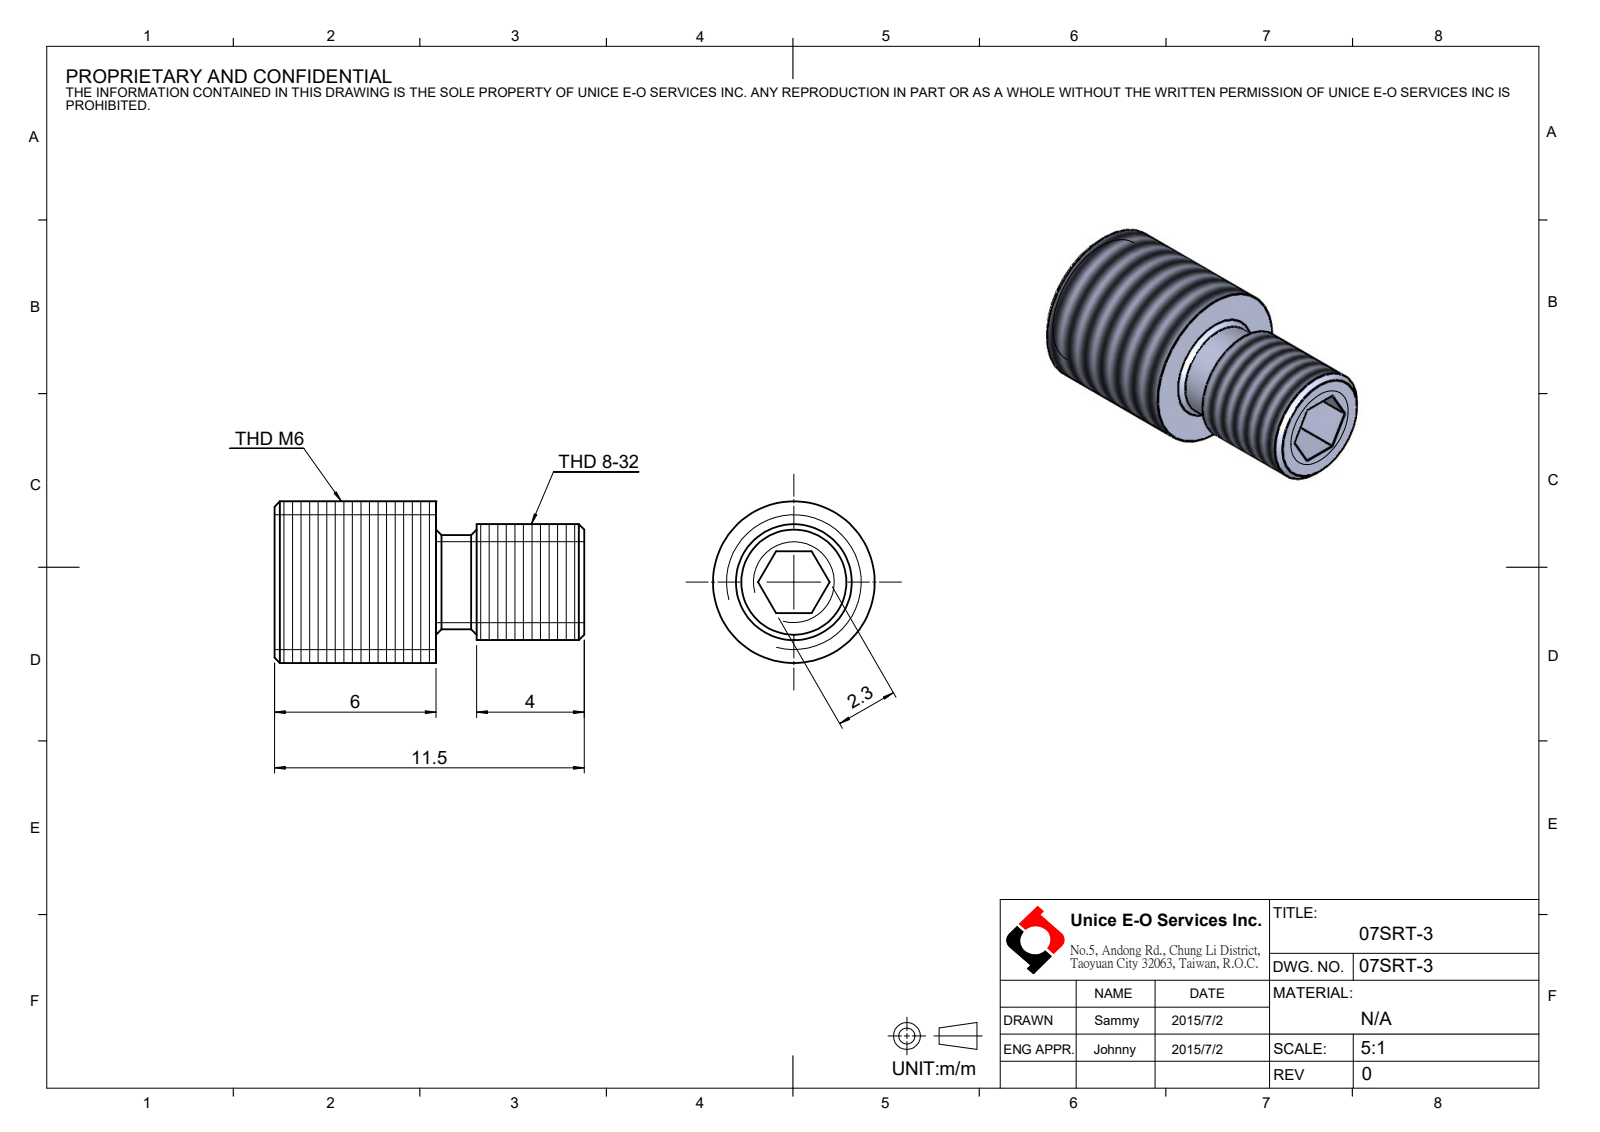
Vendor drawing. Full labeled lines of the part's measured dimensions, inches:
Part name (STEP PRODUCT): 07SRT-3
STEP written by: SolidWorks 2016 (CONFIG_CONTROL_DESIGN)
Units: inches
Bodies: 1 solid, 32 faces (18 planar, 6 cylindrical, 8 other)
Overall size (bounding box): 0.453 × 0.236 × 0.236
Volume: 0.013 in³ · Surface area: 0.451 in²
Round bosses / shafts (diameter × count): ⌀0.236 ×1, ⌀0.169 ×1, ⌀0.138 ×1
Main face-to-face distances: 0.091, 0.236, 0.118, 0.217, 0.335, 0.453, 0.098, 0.295, 0.177, 0.059
